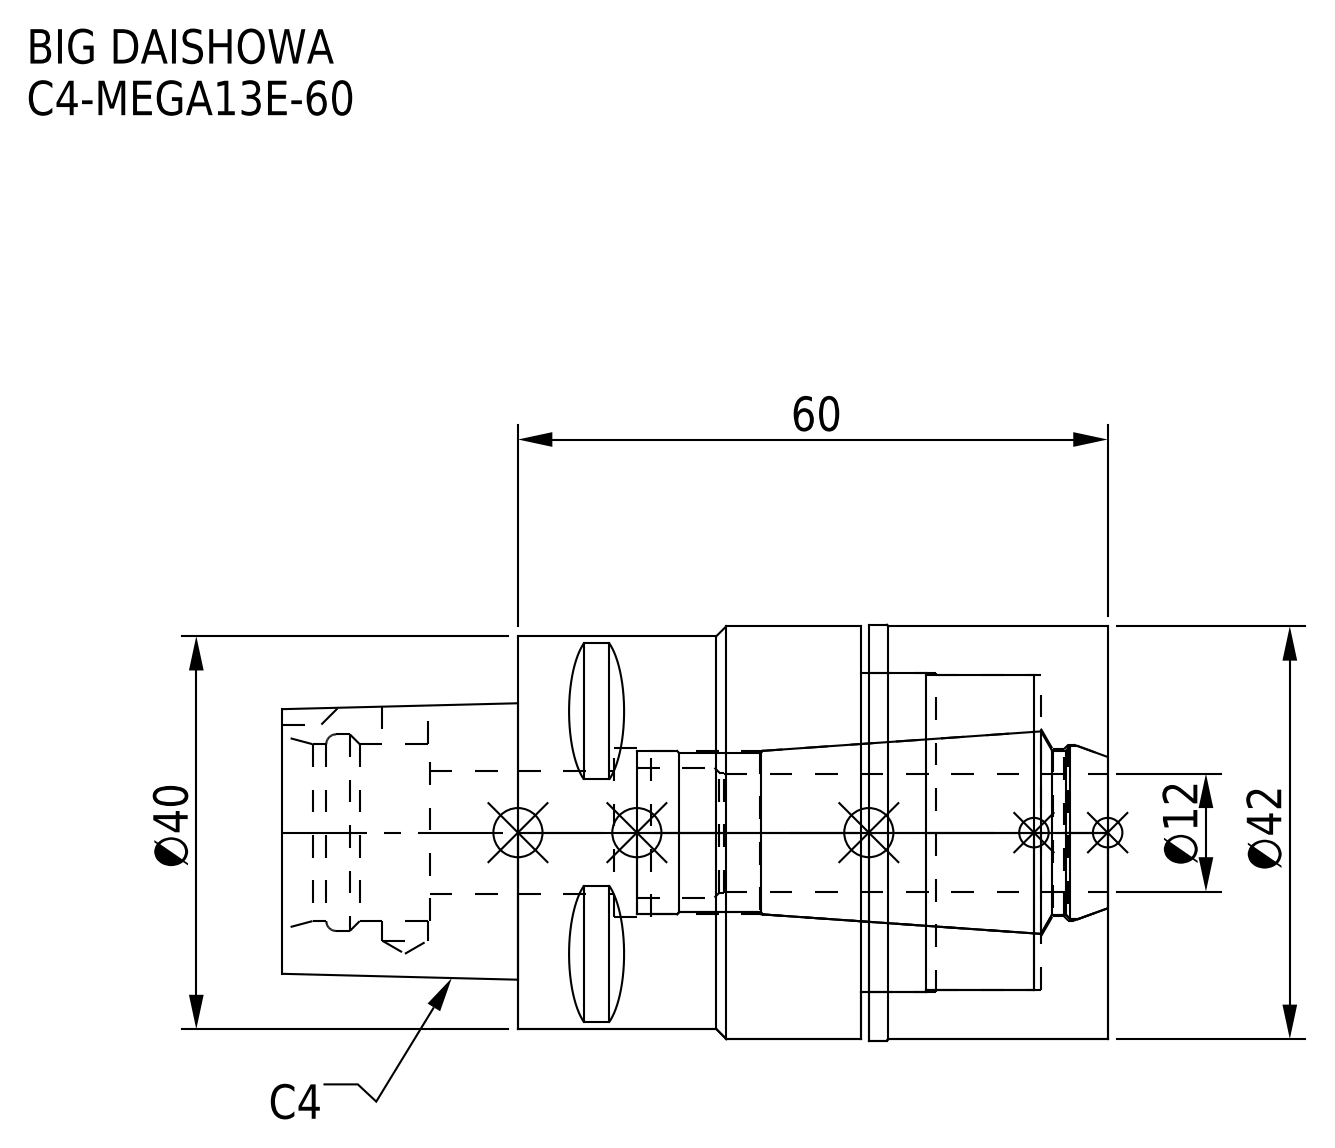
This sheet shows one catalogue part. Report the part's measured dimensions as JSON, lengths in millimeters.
{"part_name": "C4-MEGA13E-60_1.stp; MEN13_1.stp; C4-MEGA13E-60-120_ASM.stp; C4-MEGA13E-60 (+3 more)", "step_written_by": "SolidWorks 2019 (CONFIG_CONTROL_DESIGN)", "units": "millimeters", "bodies": {"solids": 2, "faces": 93, "planar": 34, "cylindrical": 37, "other": 22}, "overall_size": [84, 42.3, 42.3], "volume_mm3": 74154, "surface_area_mm2": 22562, "round_holes": [[4.6, 1], [12.5, 1], [16.6, 1], [17, 1], [17.2, 1], [17.9, 1], [18, 1], [20, 1], [32, 1], [32.5, 1]], "round_bosses_or_shafts": [[42.3, 1], [42, 1], [40, 1]], "partial_cylinders_radius": [[3, 1]], "face_to_face_distances": [25.1, 34.9, 60, 24.3, 35.7, 0.8, 6.8, 17.5, 18.3, 7.5]}
